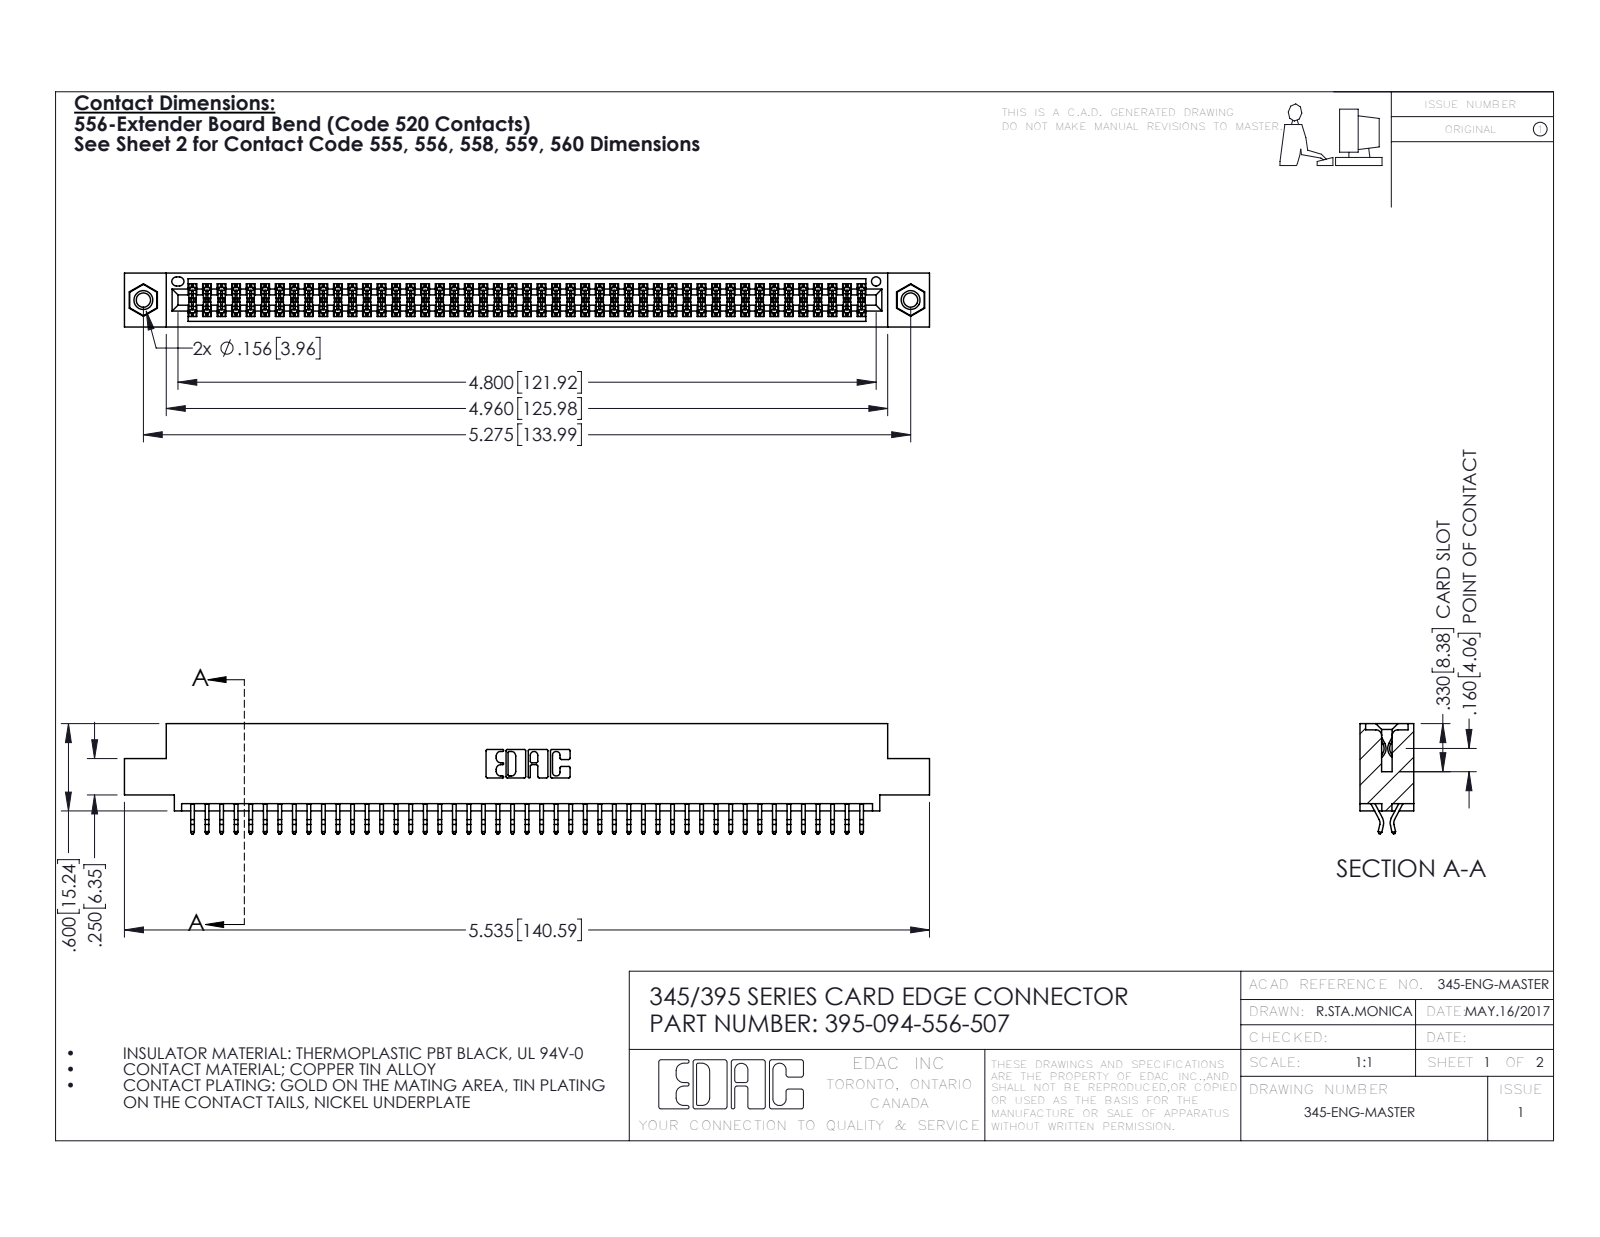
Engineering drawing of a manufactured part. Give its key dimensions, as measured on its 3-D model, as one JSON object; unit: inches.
{"part_name": "345-292-001_556 Tail; 395-094-556-507; 345 Part_0.110 Offset - 0.156 Dia-TI; 345-250-001_345-250-005-103", "step_written_by": "SolidWorks 2016 (CONFIG_CONTROL_DESIGN)", "units": "inches", "bodies": {"solids": 97, "faces": 5454, "planar": 3594, "cylindrical": 1844, "other": 16}, "overall_size": [5.535, 0.757, 0.37], "volume_in3": 0.831, "surface_area_in2": 31.4, "round_holes": [[0.098, 2], [0.125, 2], [0.156, 2], [0.064, 1]], "round_bosses_or_shafts": [[0.155, 2]], "partial_cylinders_radius": [[0.006, 141], [0.01, 22], [0.007, 6], [0.031, 6], [0.026, 3], [0.01, 2], [0.014, 2], [0.019, 2]], "face_to_face_distances": [0.072, 0.298, 0.37, 0.2, 0.025, 0.098, 0.272, 0.225, 0.175, 0.149], "hole_center_spacings": [0.27, 5.039, 5.275]}
